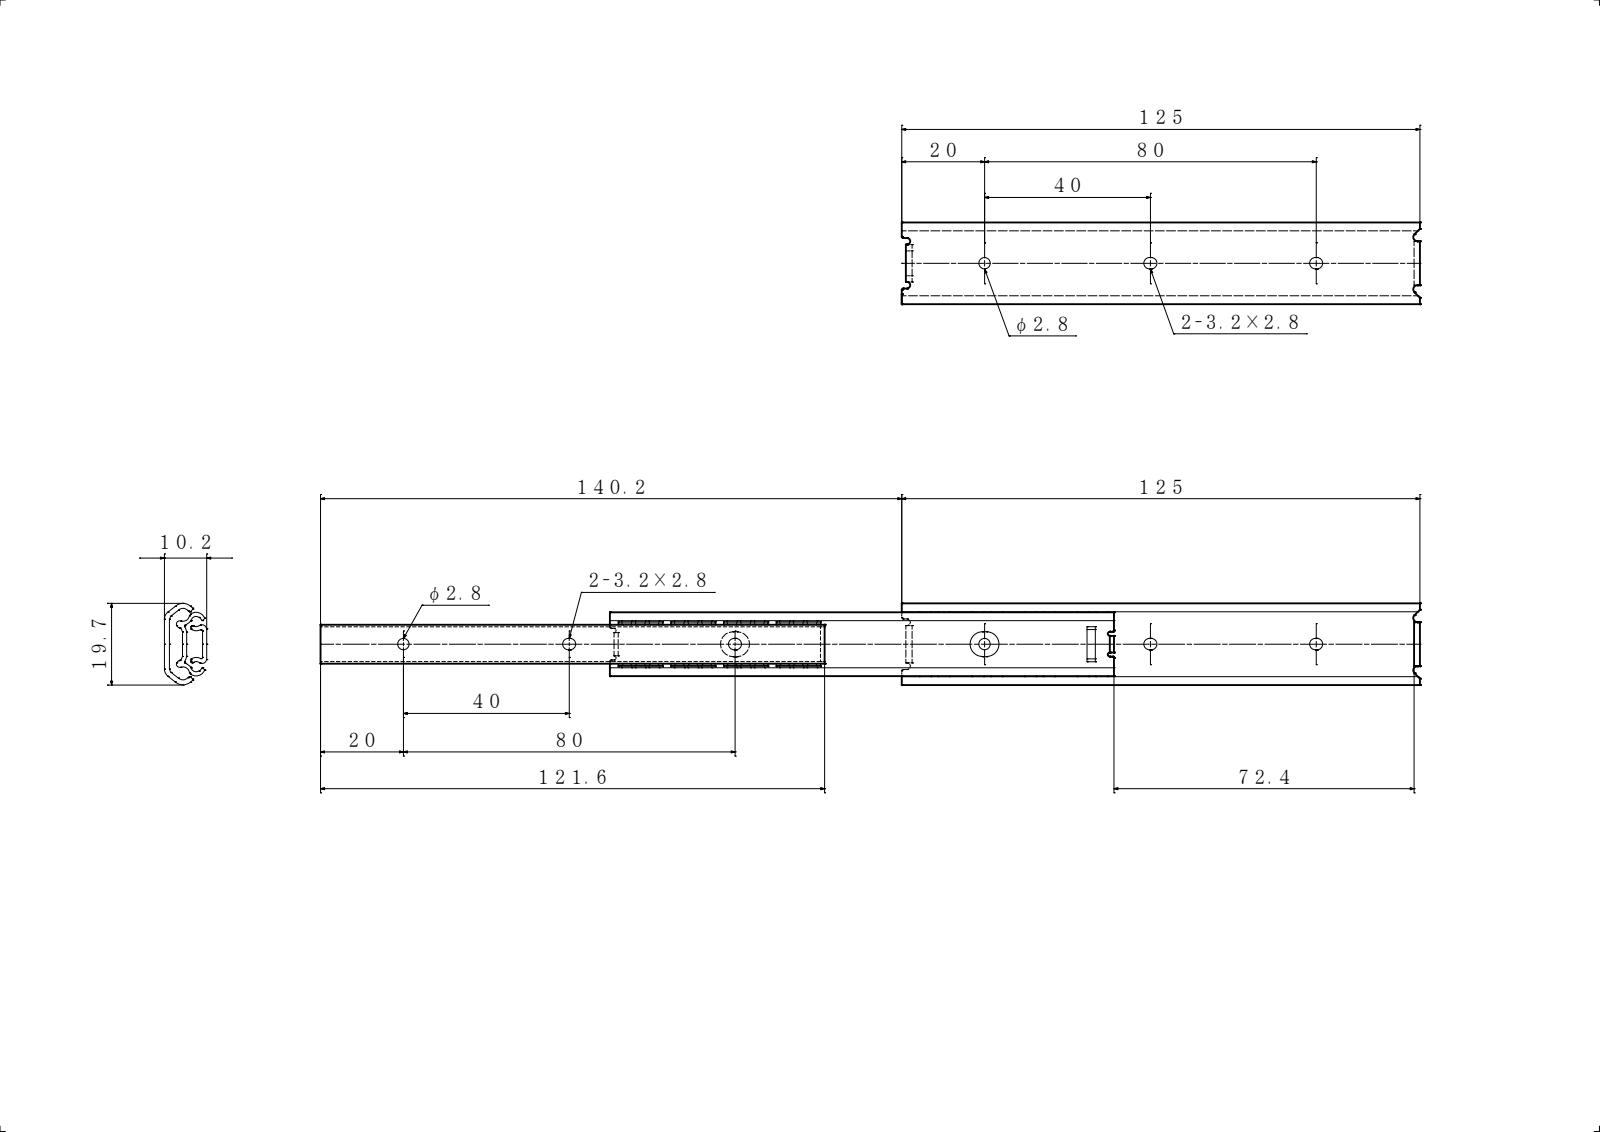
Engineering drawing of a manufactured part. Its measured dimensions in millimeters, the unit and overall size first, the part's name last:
Units: millimetres
Overall size (bounding box): 265 × 19.7 × 10.2
Round holes (diameter × count): ⌀2.8 ×2
Partial cylindrical surfaces — rounded edges, fillets, slot ends (radius × count): R0.5 ×27, R1 ×18, R0.3 ×9, R1.4 ×8, R0.1 ×4, R0.8 ×4, R1.2 ×4, R3 ×4
Main face-to-face distances: 1.2, 1, 4.84, 9, 10.2, 9.2, 8, 4.36, 3.16, 5.84
Hole centre spacings: 140
Volume: 8 978 mm³ · Surface area: 17 918 mm²
Bodies: 3 solids, 244 faces (112 planar, 132 cylindrical, 0 other)
Part name (STEP PRODUCT): UC200T-125 OM; UC200T-125 CM; UC200T-125 IM; UC200T-125
STEP written by: SolidWorks 2019 (CONFIG_CONTROL_DESIGN)
